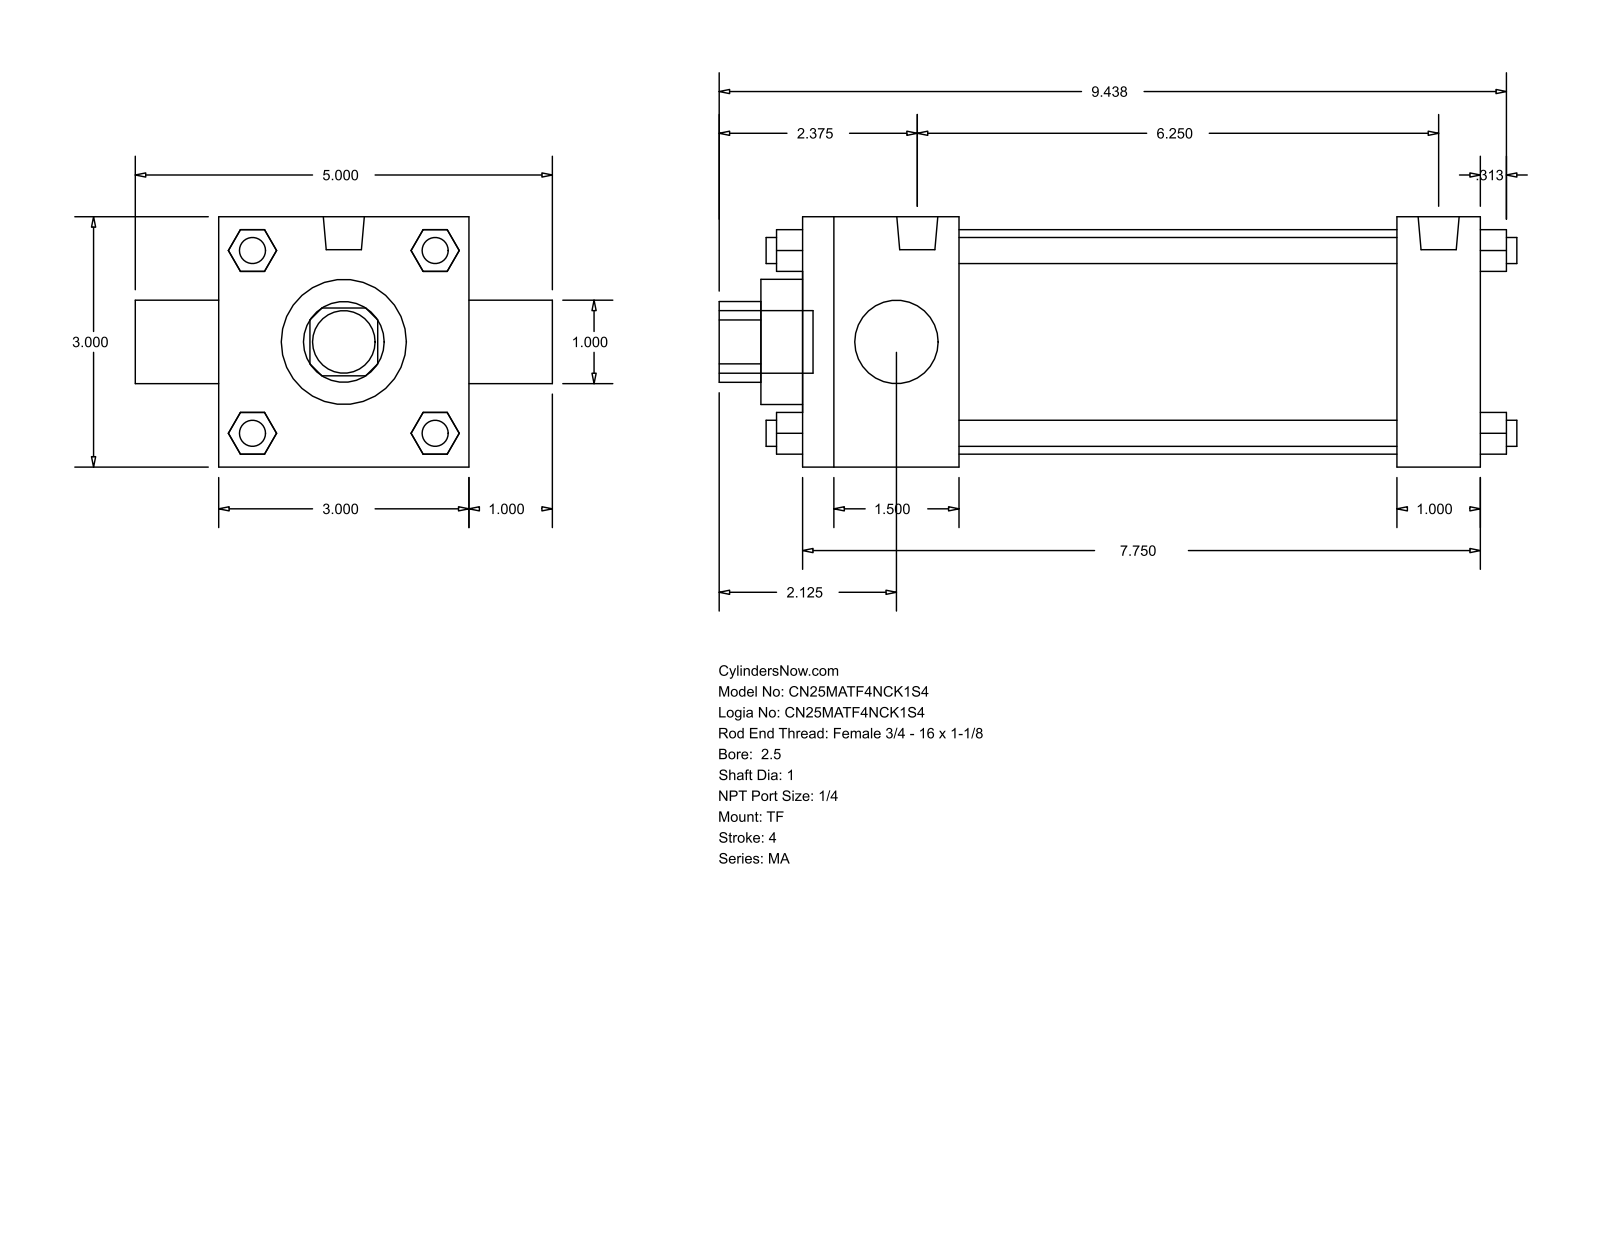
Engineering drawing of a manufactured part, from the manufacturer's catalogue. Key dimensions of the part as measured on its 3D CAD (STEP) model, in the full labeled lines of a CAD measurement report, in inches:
Part name (STEP PRODUCT): MA_TF__0250_1
STEP written by: GSSL Pune (CONFIG_CONTROL_DESIGN)
Units: inches
Bodies: 0 solids, 120 faces (92 planar, 28 cylindrical, 0 other)
Overall size (bounding box): 9.563 × 5 × 3
Round holes (diameter × count): ⌀1 ×2, ⌀1.5 ×1, ⌀2.69 ×1
Round bosses / shafts (diameter × count): ⌀0.313 ×7, ⌀0.492 ×2, ⌀0.75 ×1
Partial cylindrical surfaces — rounded edges, fillets, slot ends (radius × count): R0.484 ×1
Main face-to-face distances: 3, 8.125, 1, 0.5, 1.875, 7.125, 5.25, 6.25, 4, 1.095
